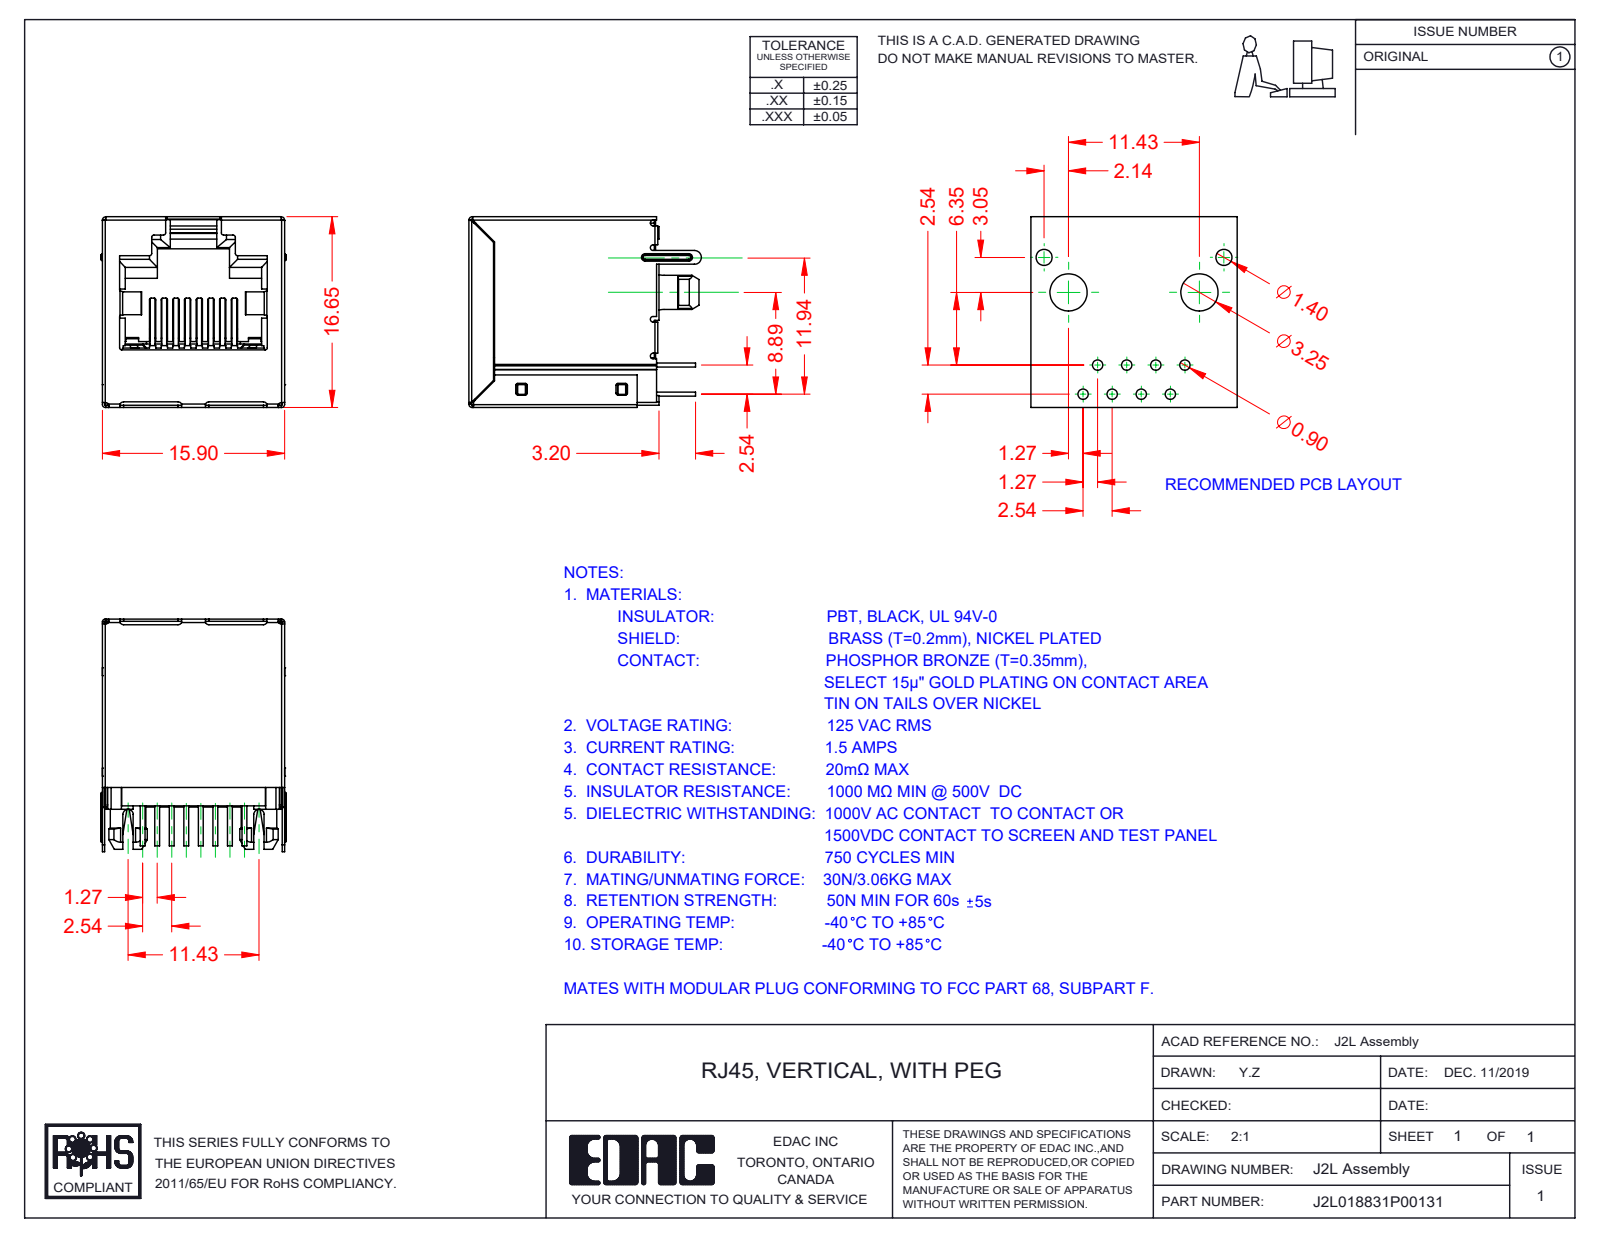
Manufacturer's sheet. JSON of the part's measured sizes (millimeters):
{"part_name": "2L Insulator; 2L Contact Lock; RJ2L018831P00131; 2L Contacts (+1 more)", "step_written_by": "SolidWorks 2016 (CONFIG_CONTROL_DESIGN)", "units": "millimeters", "bodies": {"solids": 11, "faces": 1125, "planar": 778, "cylindrical": 284, "other": 63}, "overall_size": [20.3, 16.65, 16.2], "volume_mm3": 2717, "surface_area_mm2": 6473, "round_bosses_or_shafts": [[3.1, 2], [1.1, 2]], "partial_cylinders_radius": [[0.15, 64], [0.25, 20], [0.2, 16], [0.3, 14], [0.35, 9], [0.1, 8], [0.28, 4], [0.5, 3]], "face_to_face_distances": [15.45, 15.7, 16.45, 16.2, 16.4, 15.65, 16.25, 15.9, 15.5, 1.2]}
